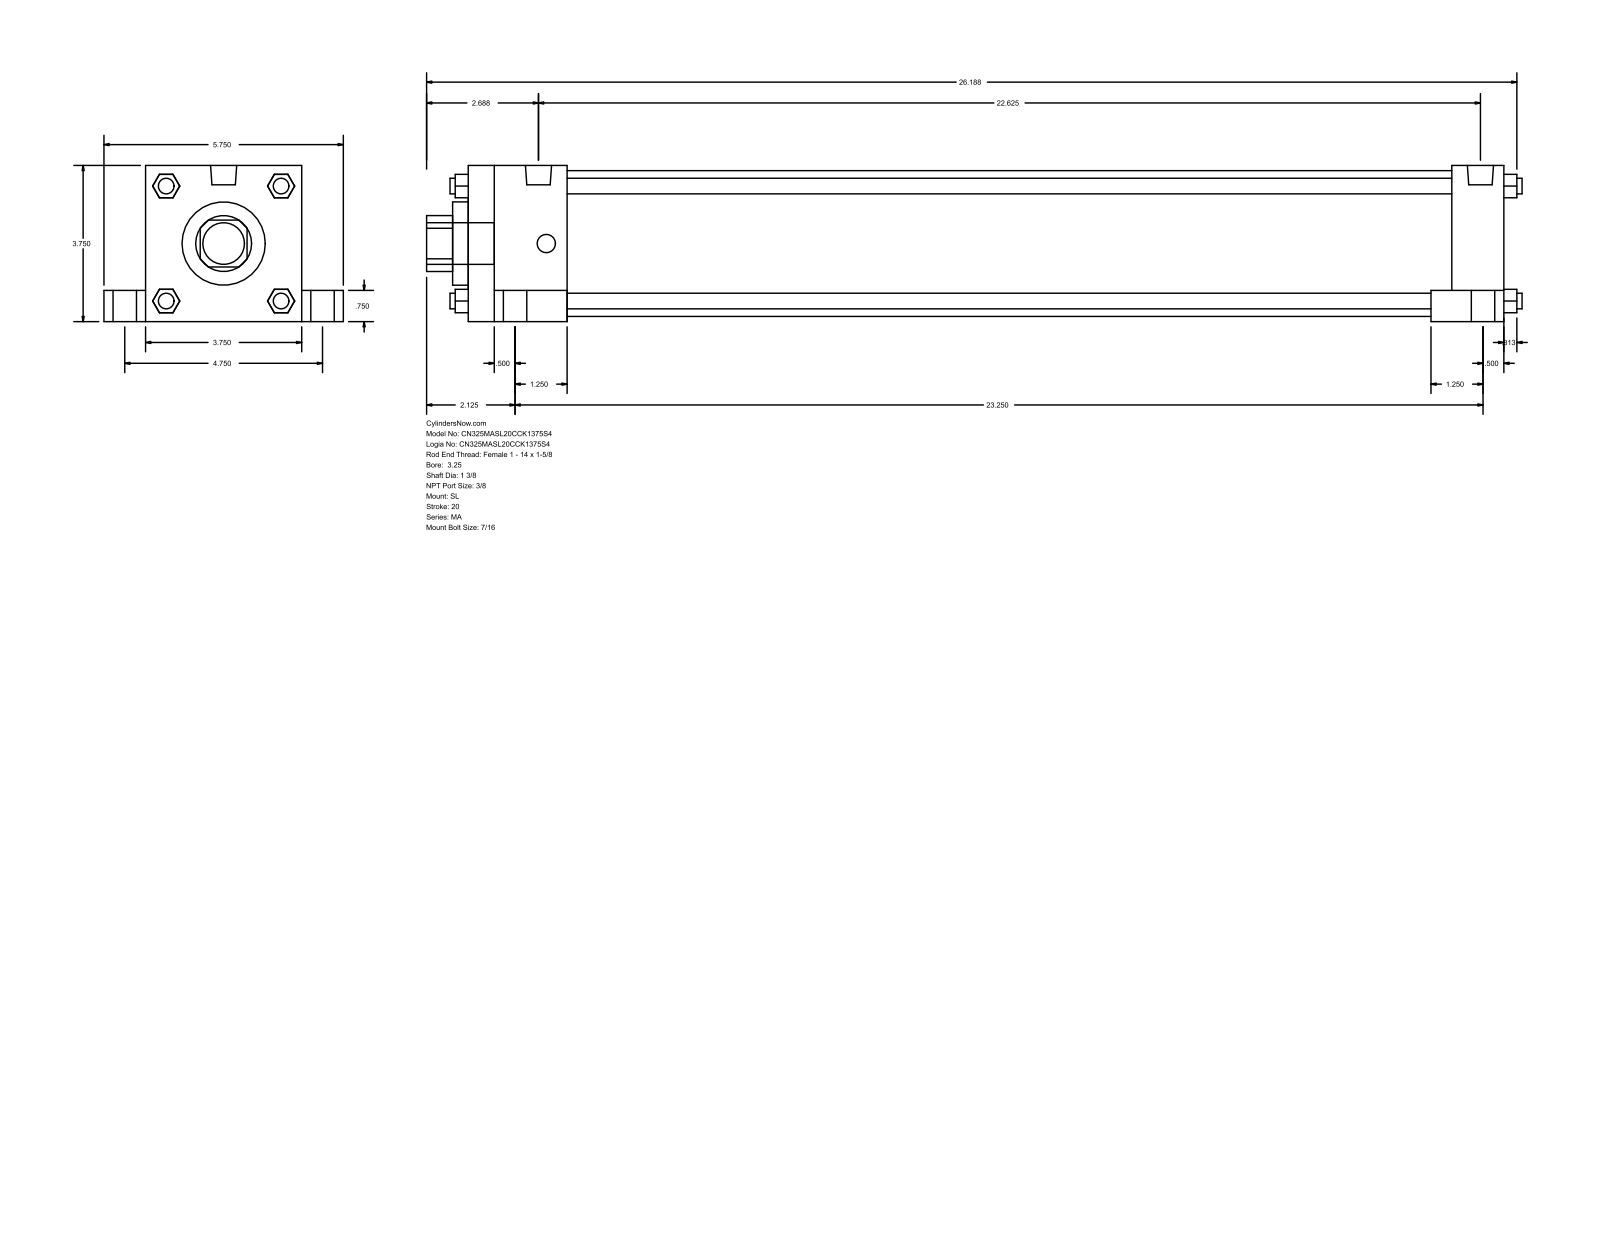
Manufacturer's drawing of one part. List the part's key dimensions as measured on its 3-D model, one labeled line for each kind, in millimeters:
Part name (STEP PRODUCT): MA_SL__0325_1.375
STEP written by: GSSL Pune (CONFIG_CONTROL_DESIGN)
Units: millimetres
Bodies: 0 solids, 148 faces (112 planar, 36 cylindrical, 0 other)
Overall size (bounding box): 668.34 × 146.05 × 95.25
Round holes (diameter × count): ⌀34.92 ×1, ⌀50.8 ×1, ⌀88.9 ×1
Round bosses / shafts (diameter × count): ⌀20.64 ×4, ⌀14.29 ×4, ⌀11.11 ×4, ⌀9.53 ×4, ⌀15.93 ×2, ⌀25.4 ×1
Partial cylindrical surfaces — rounded edges, fillets, slot ends (radius × count): R17.06 ×1
Main face-to-face distances: 95.24, 631.83, 25.41, 120.65, 600.08, 31.75, 60.32, 539.76, 571.51, 19.05
